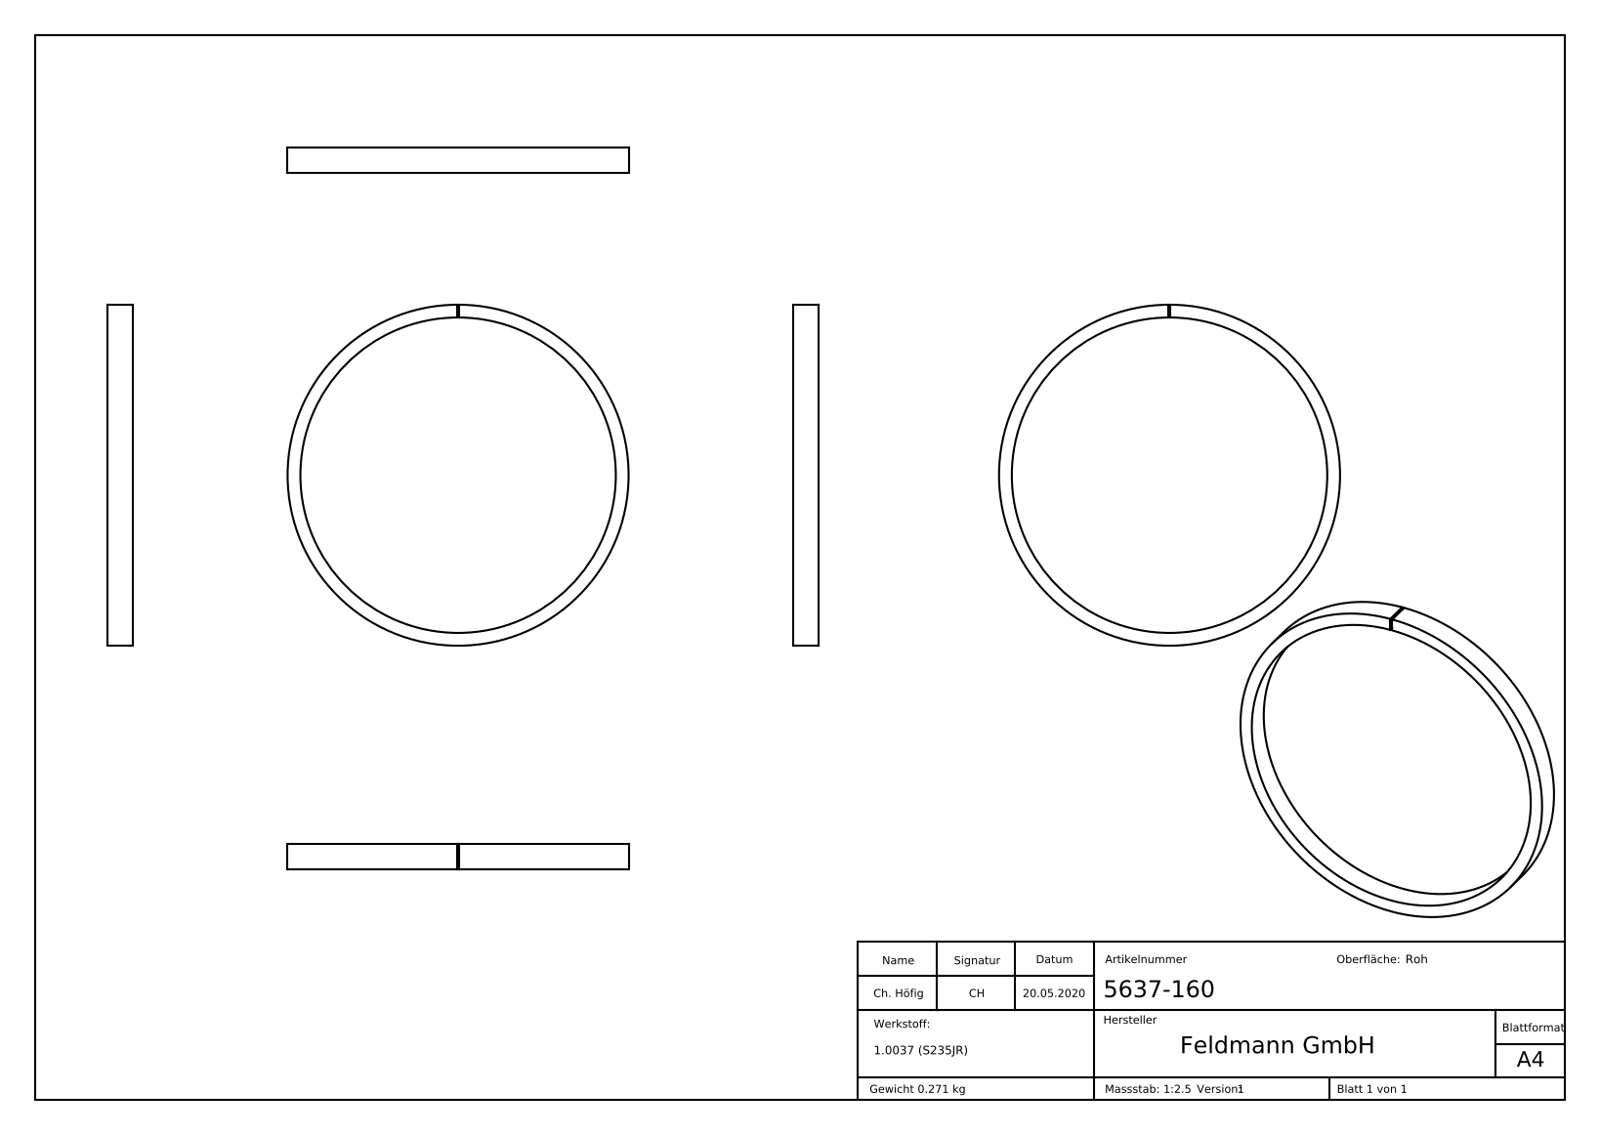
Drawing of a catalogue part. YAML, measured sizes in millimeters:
part_name: "5637-160"
step_written_by: "SolidWorks 2015 (CONFIG_CONTROL_DESIGN)"
units: millimeters
bodies: {solids: 1, faces: 210, planar: 111, cylindrical: 2, other: 97}
overall_size: [160, 160, 12]
volume: 34762
surface_area: 17530
round_holes:
  - {diameter: 148, count: 1}
round_bosses_or_shafts:
  - {diameter: 160, count: 1}
face_to_face_distances: [12, 1, 1.1, 1.78, 2.45, 0.83, 2.12, 0.99, 2.77, 1.21]
